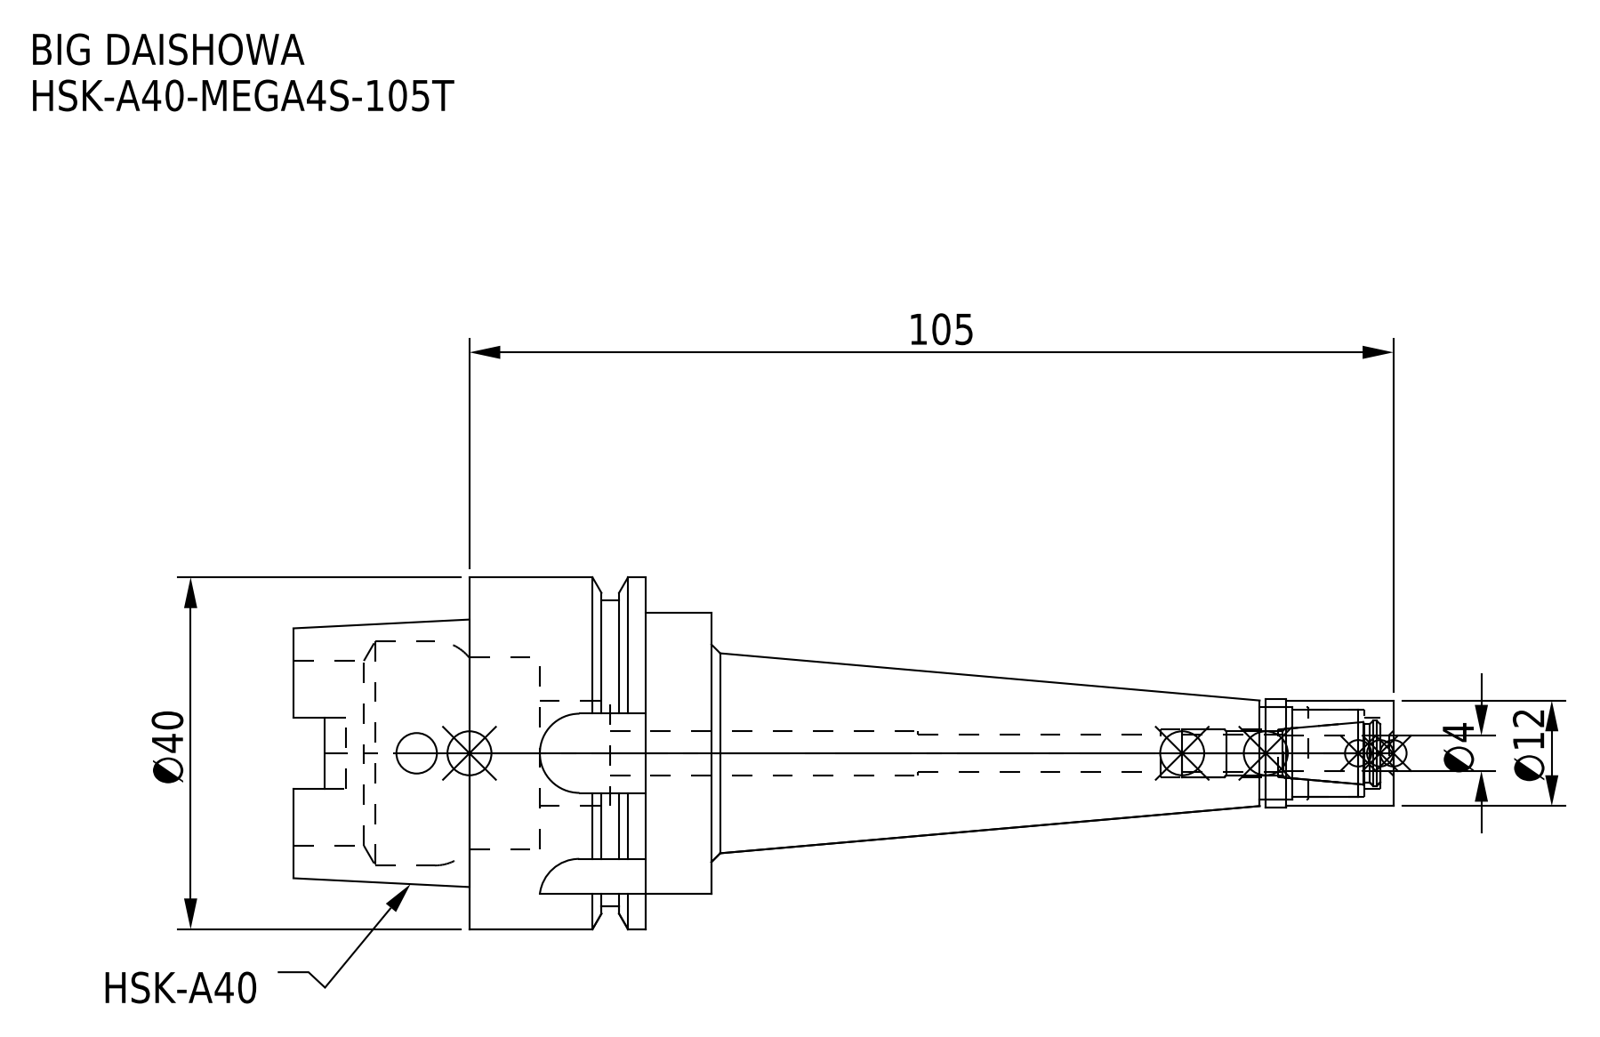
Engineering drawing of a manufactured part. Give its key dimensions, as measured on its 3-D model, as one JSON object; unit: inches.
{"part_name": "HSK-A40-MEGA4S-105T_1.stp; HSK-A40-MEGA4S-105T-040-FreeParts; MGN4S_1.stp; HSK-A40-MEGA4S-105T-040.stp (+3 more)", "step_written_by": "SolidWorks 2019 (CONFIG_CONTROL_DESIGN)", "units": "inches", "bodies": {"solids": 2, "faces": 123, "planar": 47, "cylindrical": 54, "other": 22}, "overall_size": [4.921, 1.575, 1.575], "volume_in3": 2.793, "surface_area_in2": 25.07, "round_holes": [[0.161, 1], [0.165, 1], [0.181, 1], [0.197, 1], [0.213, 1], [0.315, 1], [0.394, 1], [0.413, 1], [0.472, 1], [0.827, 1], [0.858, 1], [1.004, 1]], "round_bosses_or_shafts": [[1.575, 1], [1.37, 1], [1.26, 1], [0.484, 1]], "partial_cylinders_radius": [[0.074, 4], [0.177, 4]], "face_to_face_distances": [0.787, 0.295, 1.083, 0.313, 0.77, 0.474, 1.87, 1.575, 1.1, 1.339]}
